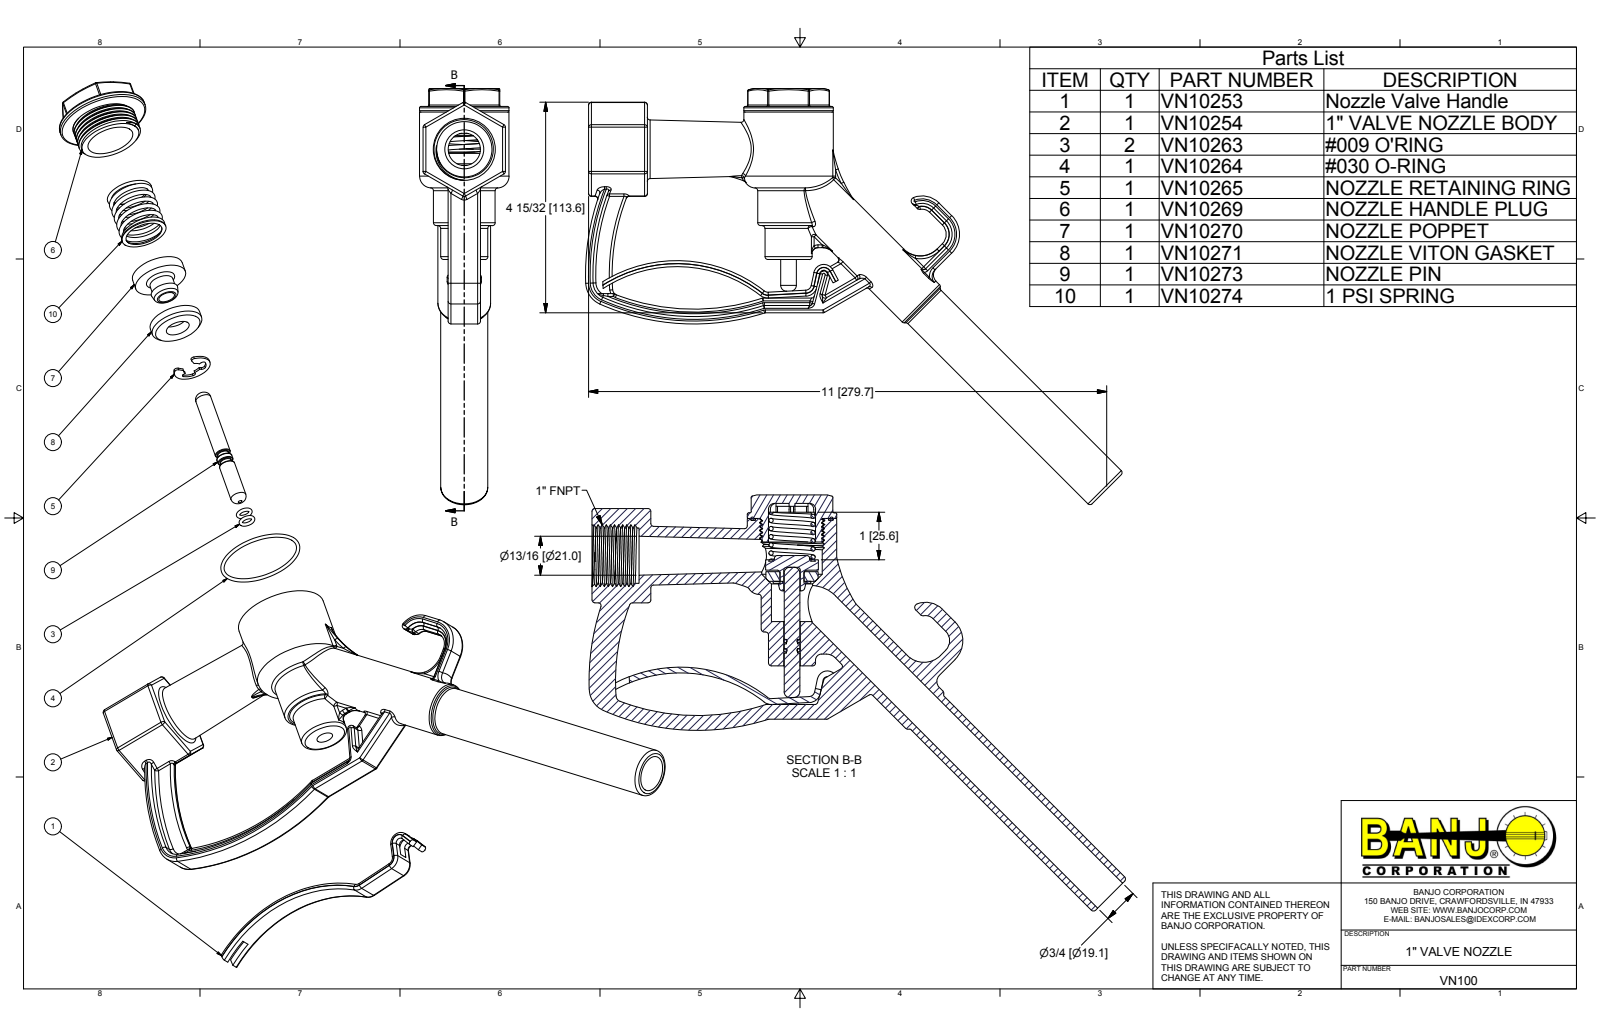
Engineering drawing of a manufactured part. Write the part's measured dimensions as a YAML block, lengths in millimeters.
part_name: "VN10254; VN10264; VN10269; VN10271 (+7 more)"
step_written_by: "Autodesk Inventor 2016 (AUTOMOTIVE_DESIGN)"
units: millimeters
bodies: {solids: 11, faces: 651, planar: 150, cylindrical: 203, other: 298}
overall_size: [289.59, 224.62, 48.26]
volume: 239094
surface_area: 107700
round_holes:
  - {diameter: 19.05, count: 2}
  - {diameter: 8.89, count: 1}
  - {diameter: 12.95, count: 1}
  - {diameter: 22.22, count: 1}
  - {diameter: 25.4, count: 1}
  - {diameter: 29.87, count: 1}
  - {diameter: 32.63, count: 1}
  - {diameter: 44.45, count: 1}
round_bosses_or_shafts:
  - {diameter: 28.45, count: 2}
  - {diameter: 48.26, count: 1}
  - {diameter: 39.37, count: 1}
  - {diameter: 34.55, count: 1}
  - {diameter: 32.26, count: 1}
  - {diameter: 28.19, count: 1}
  - {diameter: 25.4, count: 1}
  - {diameter: 8.46, count: 1}
partial_cylinders:
  - {radius: 1.52, count: 94}
  - {radius: 0.76, count: 14}
  - {radius: 1.41, count: 6}
  - {radius: 1.27, count: 4}
  - {radius: 1.98, count: 3}
  - {radius: 3.17, count: 3}
  - {radius: 6.35, count: 2}
  - {radius: 8.73, count: 2}
face_to_face_distances: [12.7, 44.45, 20.24, 24.2, 31.75, 41.4, 6.75, 44.44, 25.4, 4.76]
